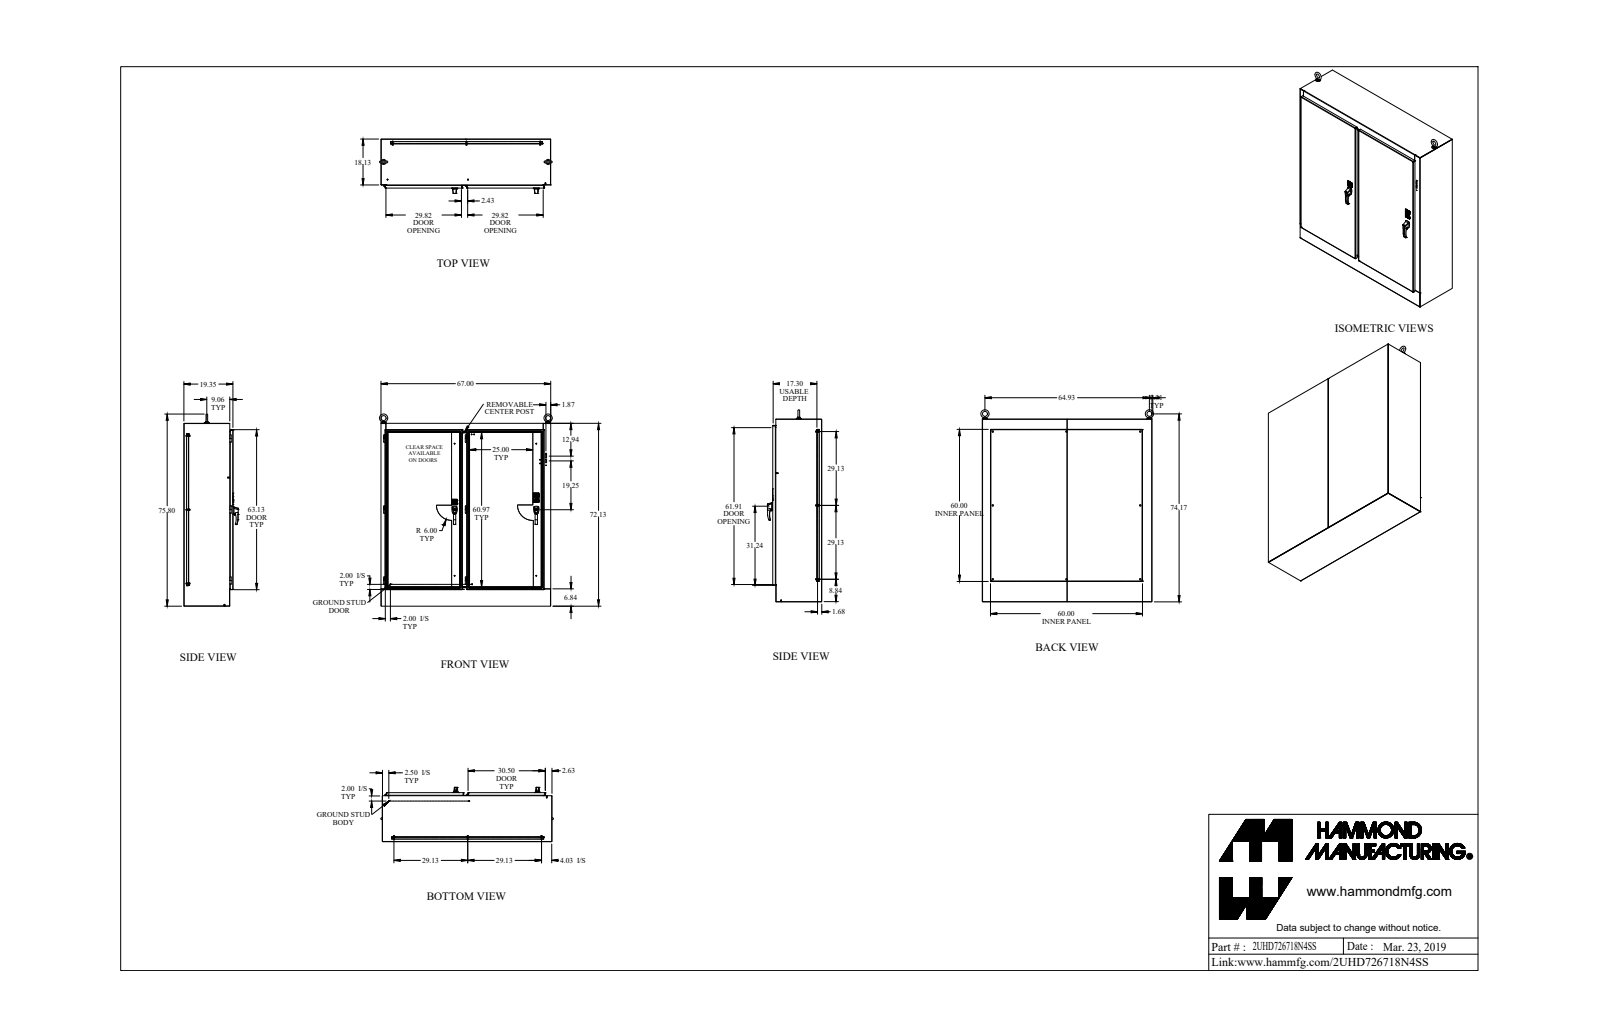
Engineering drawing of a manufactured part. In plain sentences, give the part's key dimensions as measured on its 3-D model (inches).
The part is named "2UHD726718N4SS". Its 3-D file was written by "SolidWorks 2018 (AUTOMOTIVE_DESIGN)". It is 222 solids with 3293 faces: 1924 planar, 982 cylindrical and 387 other. Overall it measures 75.799 by 68.182 by 21.466 inches. Its volume is 5 486 cubic inches and its surface area 44 070 square inches. Round holes: 13 of diameter 0.196, 12 of diameter 0.25, 9 of diameter 0.281, 9 of diameter 0.307, 8 of diameter 0.35, 6 of diameter 0.257, 6 of diameter 0.313, 5 of diameter 0.255, 5 of diameter 0.445, 4 of diameter 0.156, 4 of diameter 0.28, 4 of diameter 0.282. Round bosses or shafts: 18 of diameter 0.25, 14 of diameter 1, 9 of diameter 0.65, 8 of diameter 0.375, 8 of diameter 0.332, 6 of diameter 0.75, 6 of diameter 0.625, 6 of diameter 0.5. Partial cylindrical surfaces (rounded edges, fillets, slot ends): 67 of radius 0.125, 34 of radius 0.048, 34 of radius 0.143, 34 of radius 0.5, 32 of radius 0.017, 28 of radius 0.03, 27 of radius 0.06, 26 of radius 0.25. The main face-to-face distances are 0.095, 1, 18.368, 19.368, 18.273, 19.273, 0.072, 1.907, 1.812, 16.461. The hole center spacings are 58.25, 29.125, 29.125, 65.125, 65.126, 1, 32.25, 0.688.
